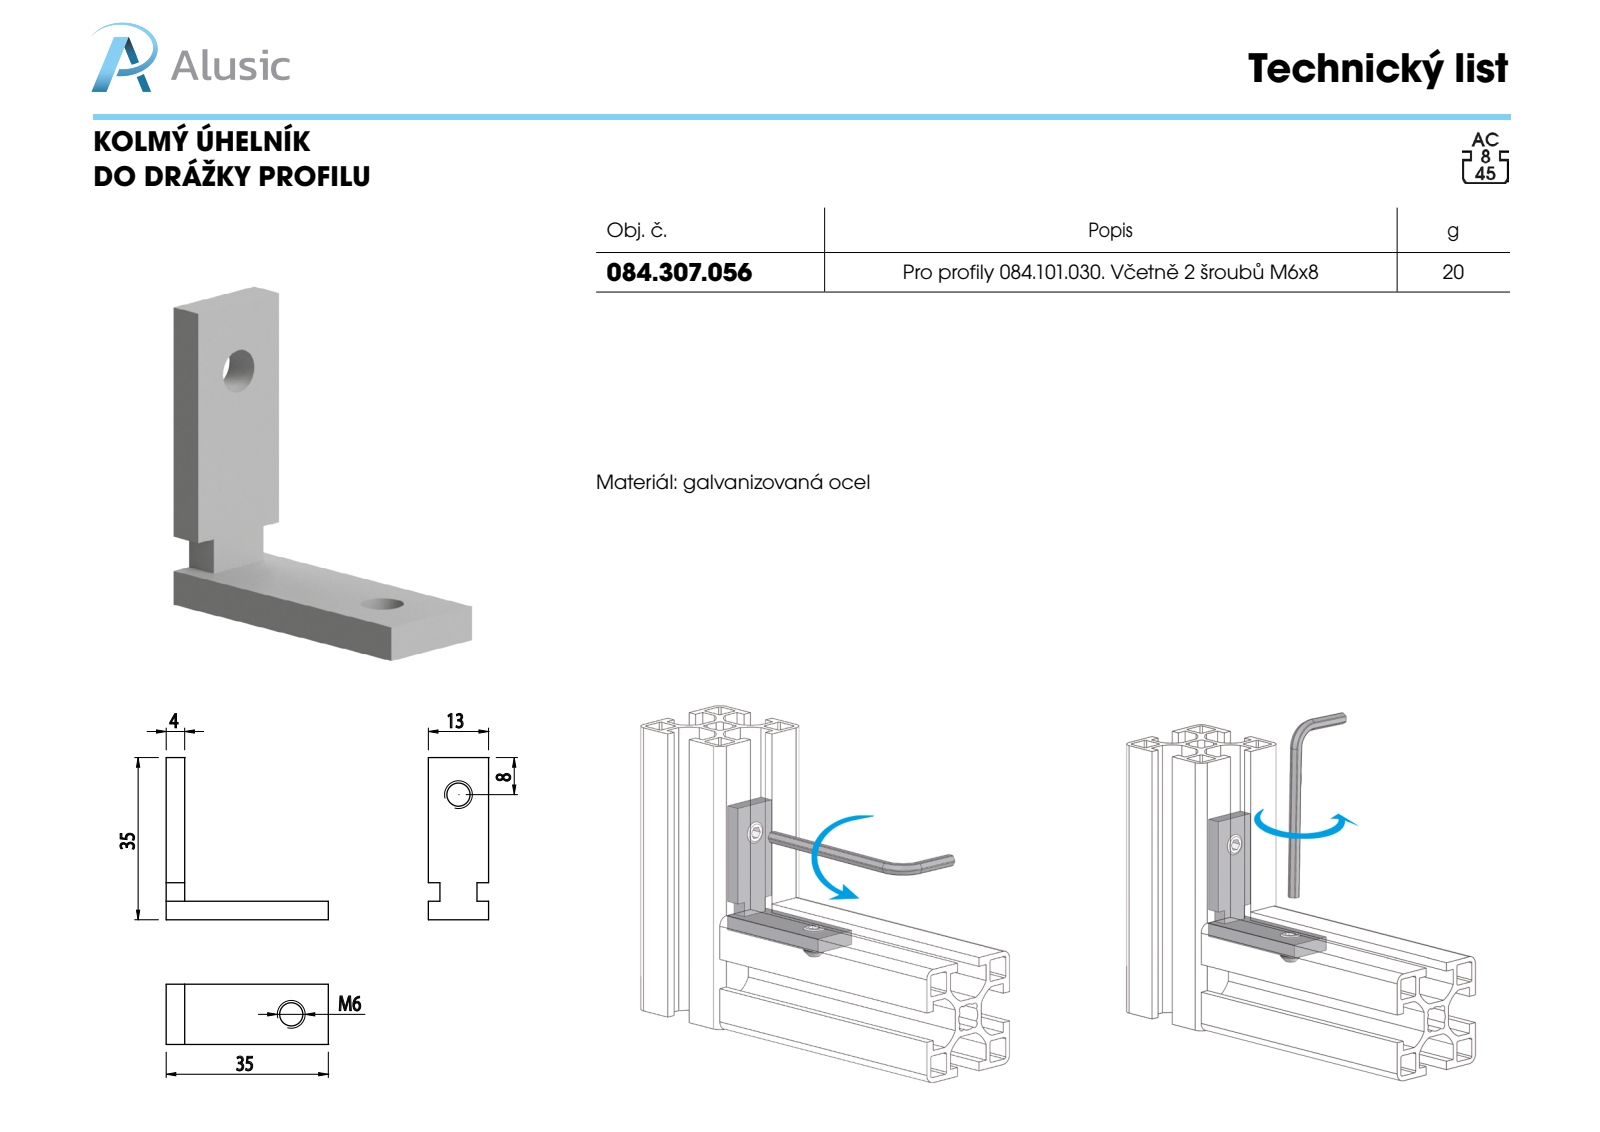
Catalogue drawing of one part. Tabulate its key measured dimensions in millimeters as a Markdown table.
| quantity | value |
| --- | --- |
| part name | 084.307.056 |
| STEP written by | SolidWorks 2016 (CONFIG_CONTROL_DESIGN) |
| units | millimeters |
| bodies | 1 solid, 18 faces (14 planar, 4 cylindrical, 0 other) |
| overall size | 35 × 35 × 13 |
| volume | 3 195 mm³ |
| surface area | 2 395 mm² |
| round holes (diameter × count) | 5 × 2 |
| main face-to-face distances | 4, 13, 35, 31, 8, 2.5, 10.5, 27 |
